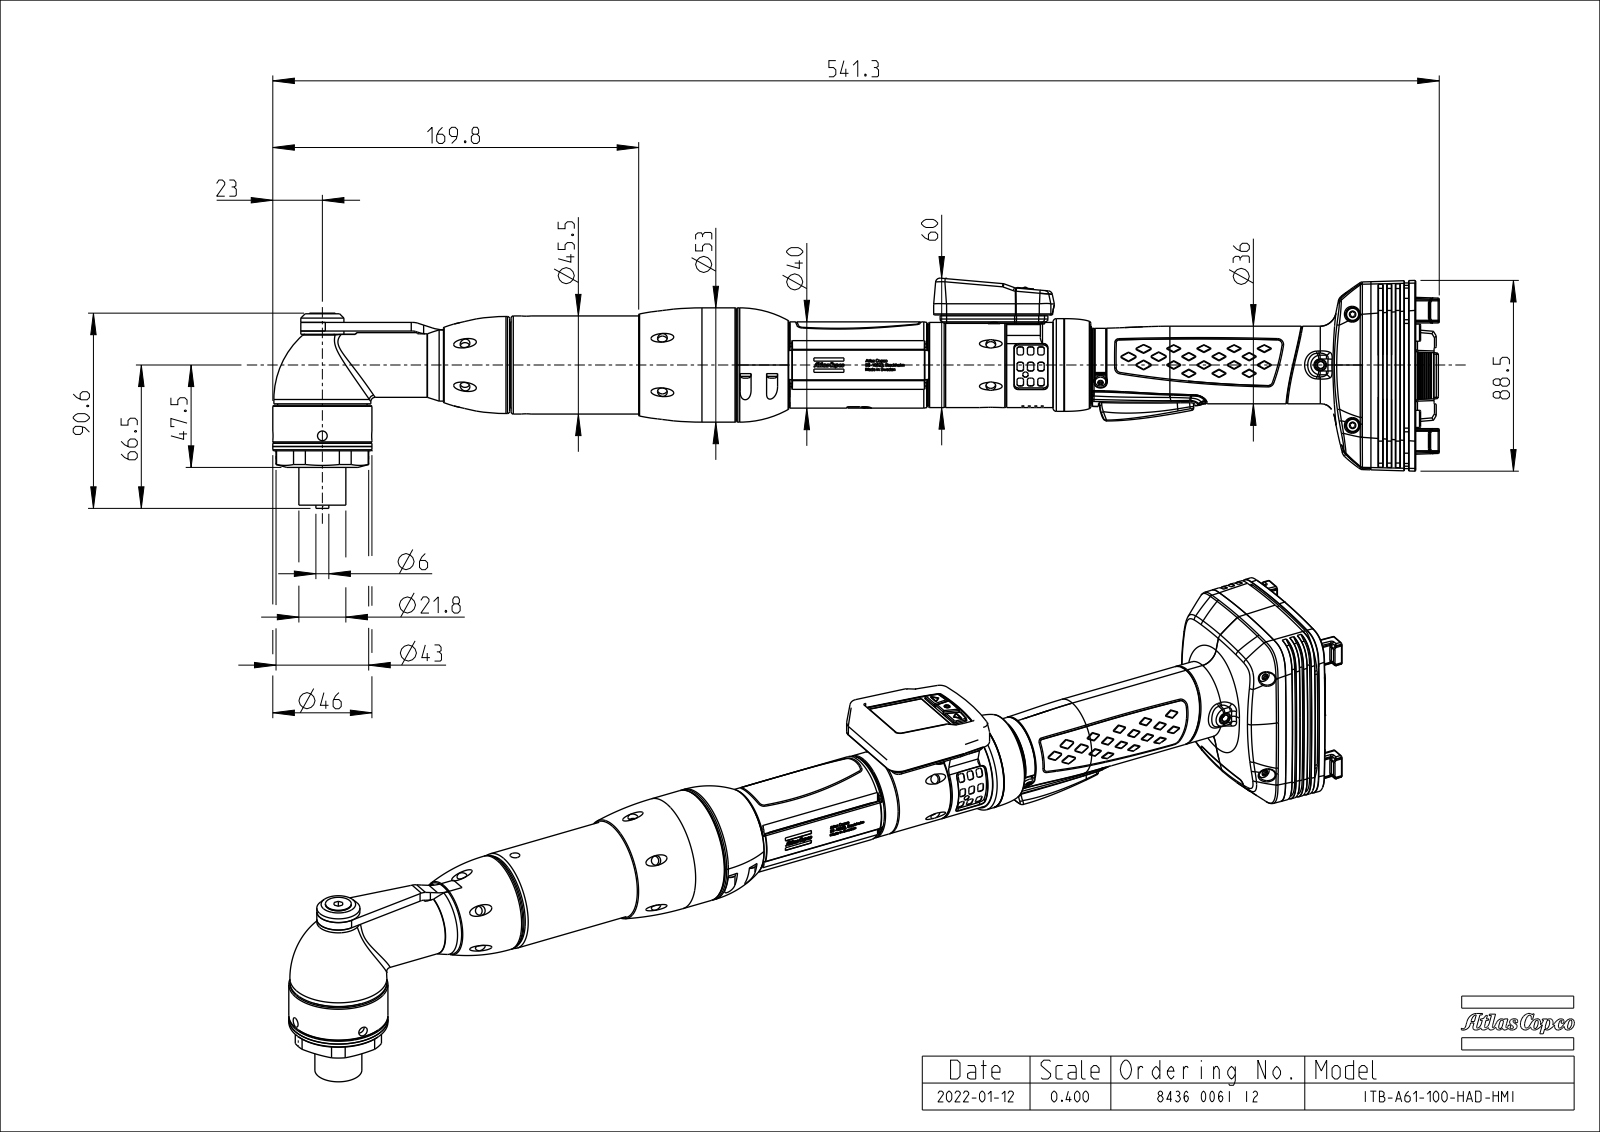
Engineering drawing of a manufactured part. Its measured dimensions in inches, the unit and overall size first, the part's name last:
Units: inches
Overall size (bounding box): 21.311 × 4.145 × 2.934
Round holes (diameter × count): ⌀0.177 ×13, ⌀0.039 ×12, ⌀0.126 ×10, ⌀0.098 ×9, ⌀0.081 ×4, ⌀0.087 ×4, ⌀0.106 ×4, ⌀0.13 ×4, ⌀0.169 ×4, ⌀0.118 ×3, ⌀0.157 ×3, ⌀0.063 ×2
Round bosses / shafts (diameter × count): ⌀0.138 ×3, ⌀1.772 ×2, ⌀2.087 ×1, ⌀1.988 ×1, ⌀1.811 ×1, ⌀1.791 ×1, ⌀1.693 ×1, ⌀1.634 ×1
Partial cylindrical surfaces — rounded edges, fillets, slot ends (radius × count): R0.012 ×529, R0.008 ×230, R0.02 ×209, R0.039 ×132, R0.079 ×110, R0.004 ×36, R0.059 ×30, R0.118 ×29
Main face-to-face distances: 0.098, 0.199, 0.079, 0.795, 0.039, 0.118, 0.697, 0.874, 0.433, 0.909
Hole centre spacings: 0.118, 0.236, 0.75, 2.184, 2.294, 3.077, 0.354, 3.606
Volume: 42.86 in³ · Surface area: 325.5 in²
Bodies: 6 solids, 11782 faces (4416 planar, 2537 cylindrical, 4829 other)
Part name (STEP PRODUCT): EXT_COMP_SW0012
STEP written by: CREO PARAMETRIC BY PTC INC, 2020281 (CONFIG_CONTROL_DESIGN)
